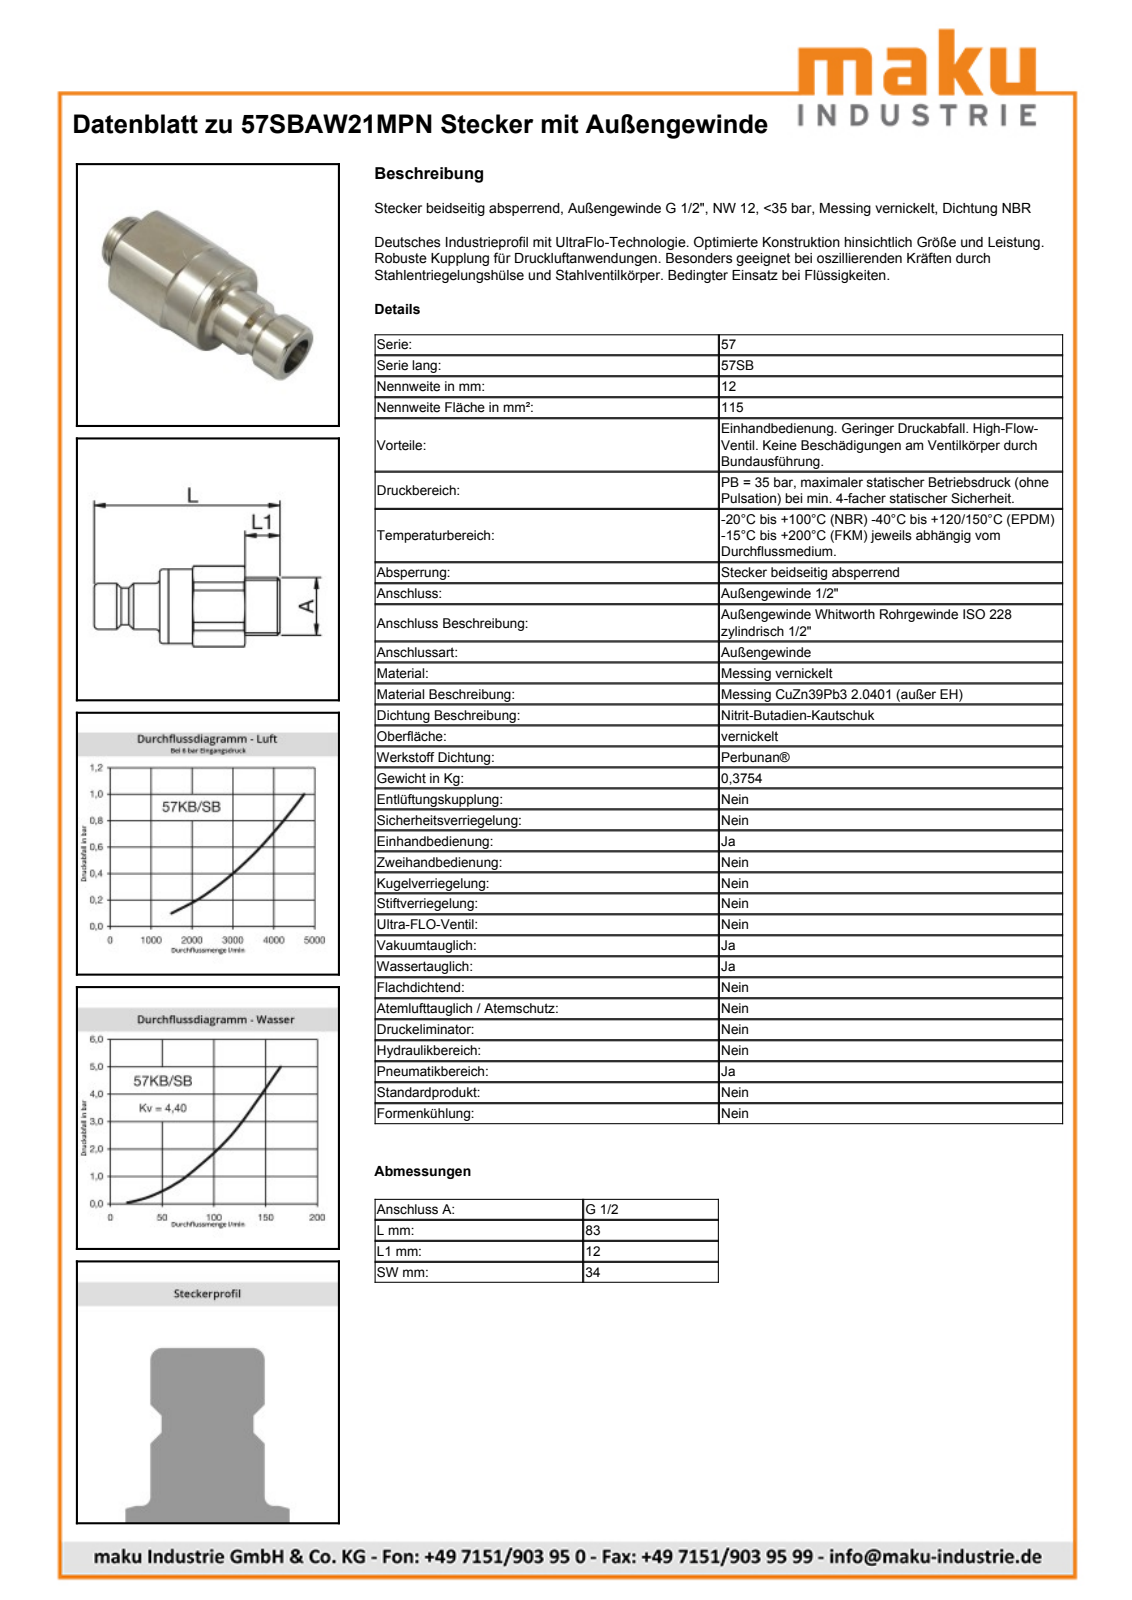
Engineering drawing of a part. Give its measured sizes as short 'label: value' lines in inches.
name: D105912
written by: Autodesk Inventor 2011 (AUTOMOTIVE_DESIGN)
unit: in
bodies: 1 solid, 60 faces (19 planar, 19 cylindrical, 22 other)
size: 3.268 × 1.457 × 1.36
volume: 3.23 in³; area: 16.51 in²
holes: 1× ⌀0.835, 1× ⌀1.14
bosses: 1× ⌀1.339, 1× ⌀1.138, 1× ⌀1.118, 1× ⌀1.069, 1× ⌀1.004, 1× ⌀0.825, 1× ⌀0.823, 1× ⌀0.661
rounds: 1× R0.728
face distances: 1.339, 1.339, 0.472, 1.614, 2.087, 1.181, 2.795, 3.268, 2.874, 1.693
